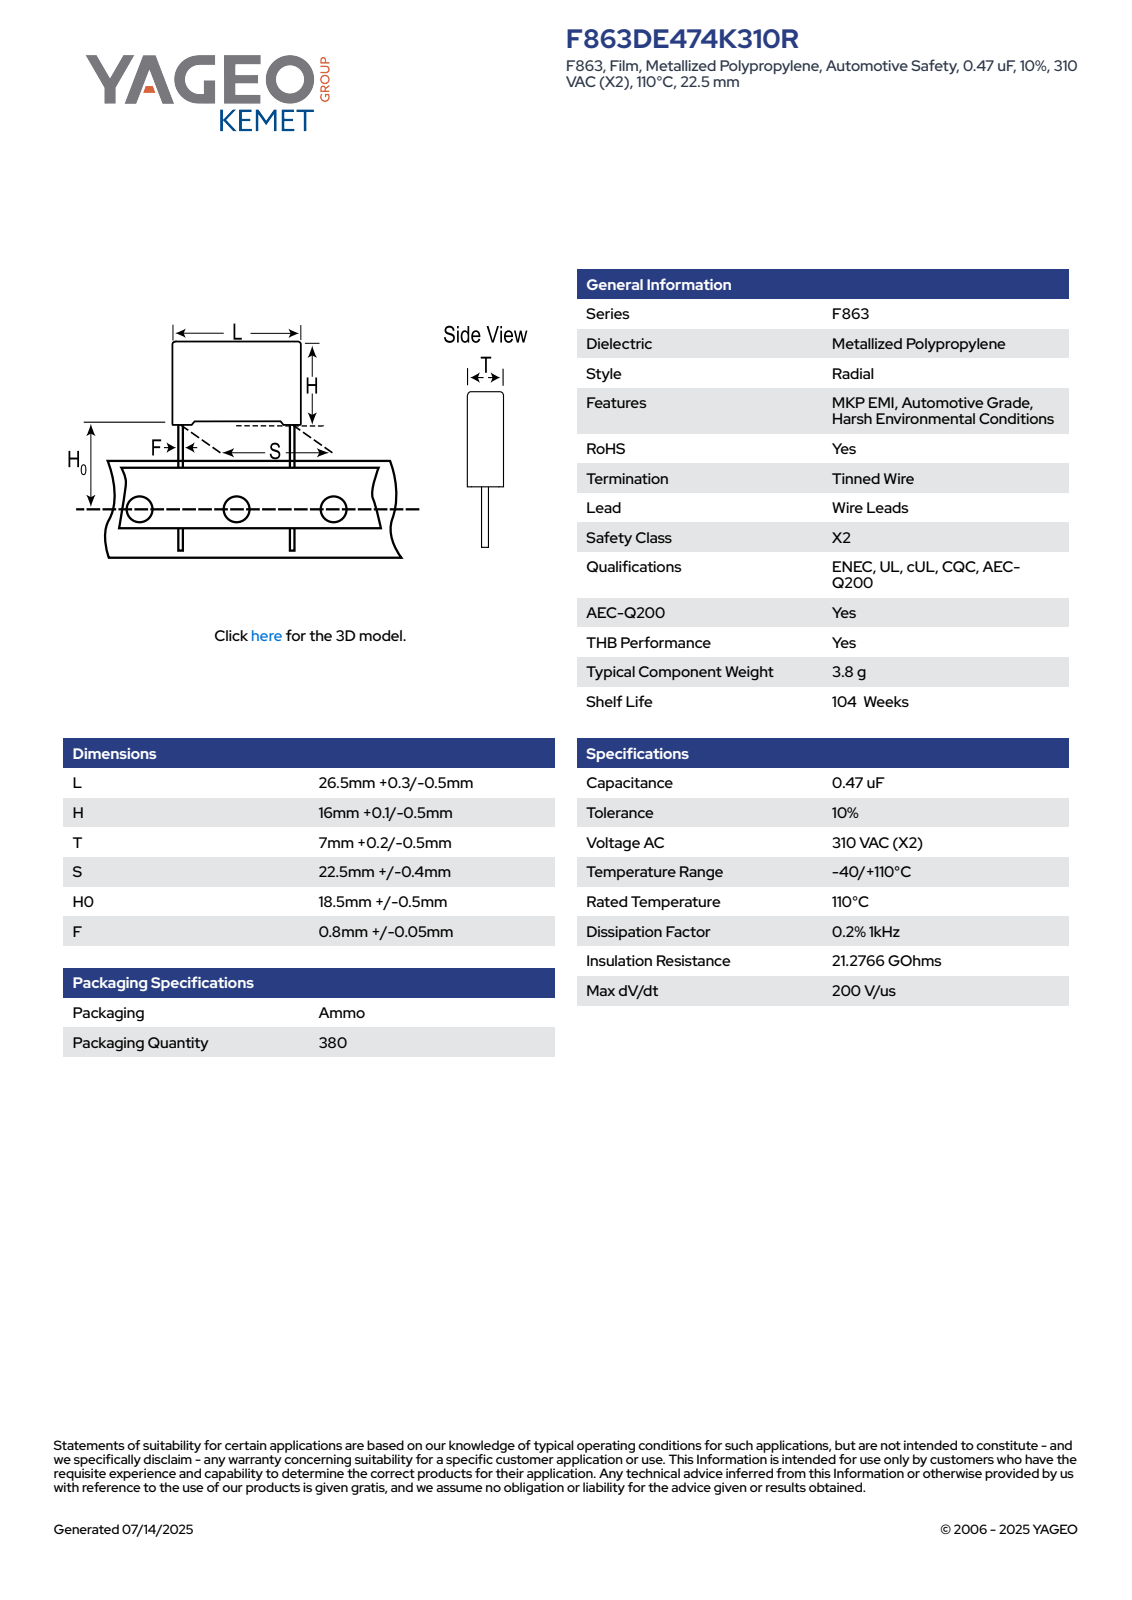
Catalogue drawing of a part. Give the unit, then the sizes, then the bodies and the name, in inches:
Units: inches
Overall size (bounding box): 1.382 × 1.055 × 0.284
Round bosses / shafts (diameter × count): ⌀0.033 ×2
Partial cylindrical surfaces — rounded edges, fillets, slot ends (radius × count): R0.02 ×4
Main face-to-face distances: 0.283, 0.604, 1.055, 0.612, 0.035, 0.03, 0.022, 0.634, 0.248, 0.213
Volume: 0.183 in³ · Surface area: 2.527 in²
Bodies: 4 solids, 85 faces (77 planar, 8 cylindrical, 0 other)
Part name (STEP PRODUCT): CFR_RB2_26.5X16X7_L26.8H16.1T7.2S22.5H019F0.85
STEP written by: SolidWorks 2020 (AUTOMOTIVE_DESIGN)
